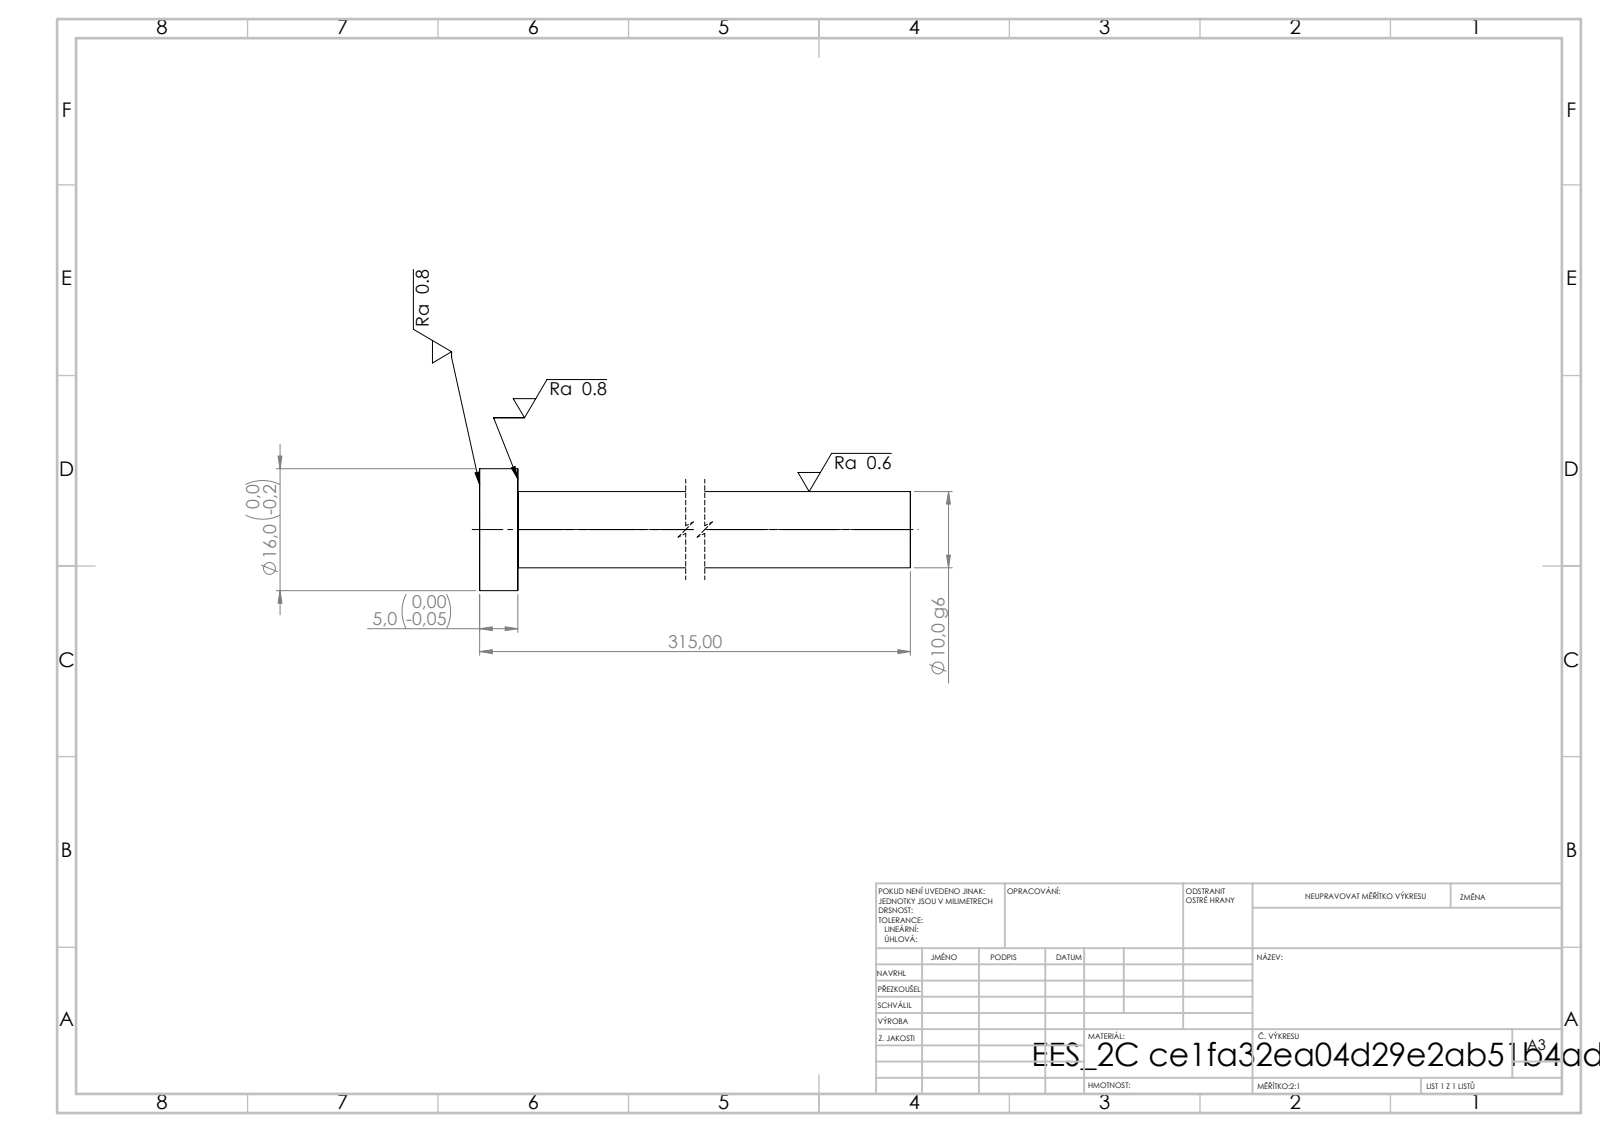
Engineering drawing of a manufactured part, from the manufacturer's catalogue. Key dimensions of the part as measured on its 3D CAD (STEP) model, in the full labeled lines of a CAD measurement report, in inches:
STEP written by: SolidWorks 2019 (CONFIG_CONTROL_DESIGN)
Units: inches
Bodies: 1 solid, 7 faces (3 planar, 4 cylindrical, 0 other)
Overall size (bounding box): 12.402 × 0.63 × 0.63
Volume: 1.547 in³ · Surface area: 16.11 in²
Round bosses / shafts (diameter × count): ⌀0.63 ×1, ⌀0.394 ×1
Main face-to-face distances: 0.197, 12.402, 12.205
